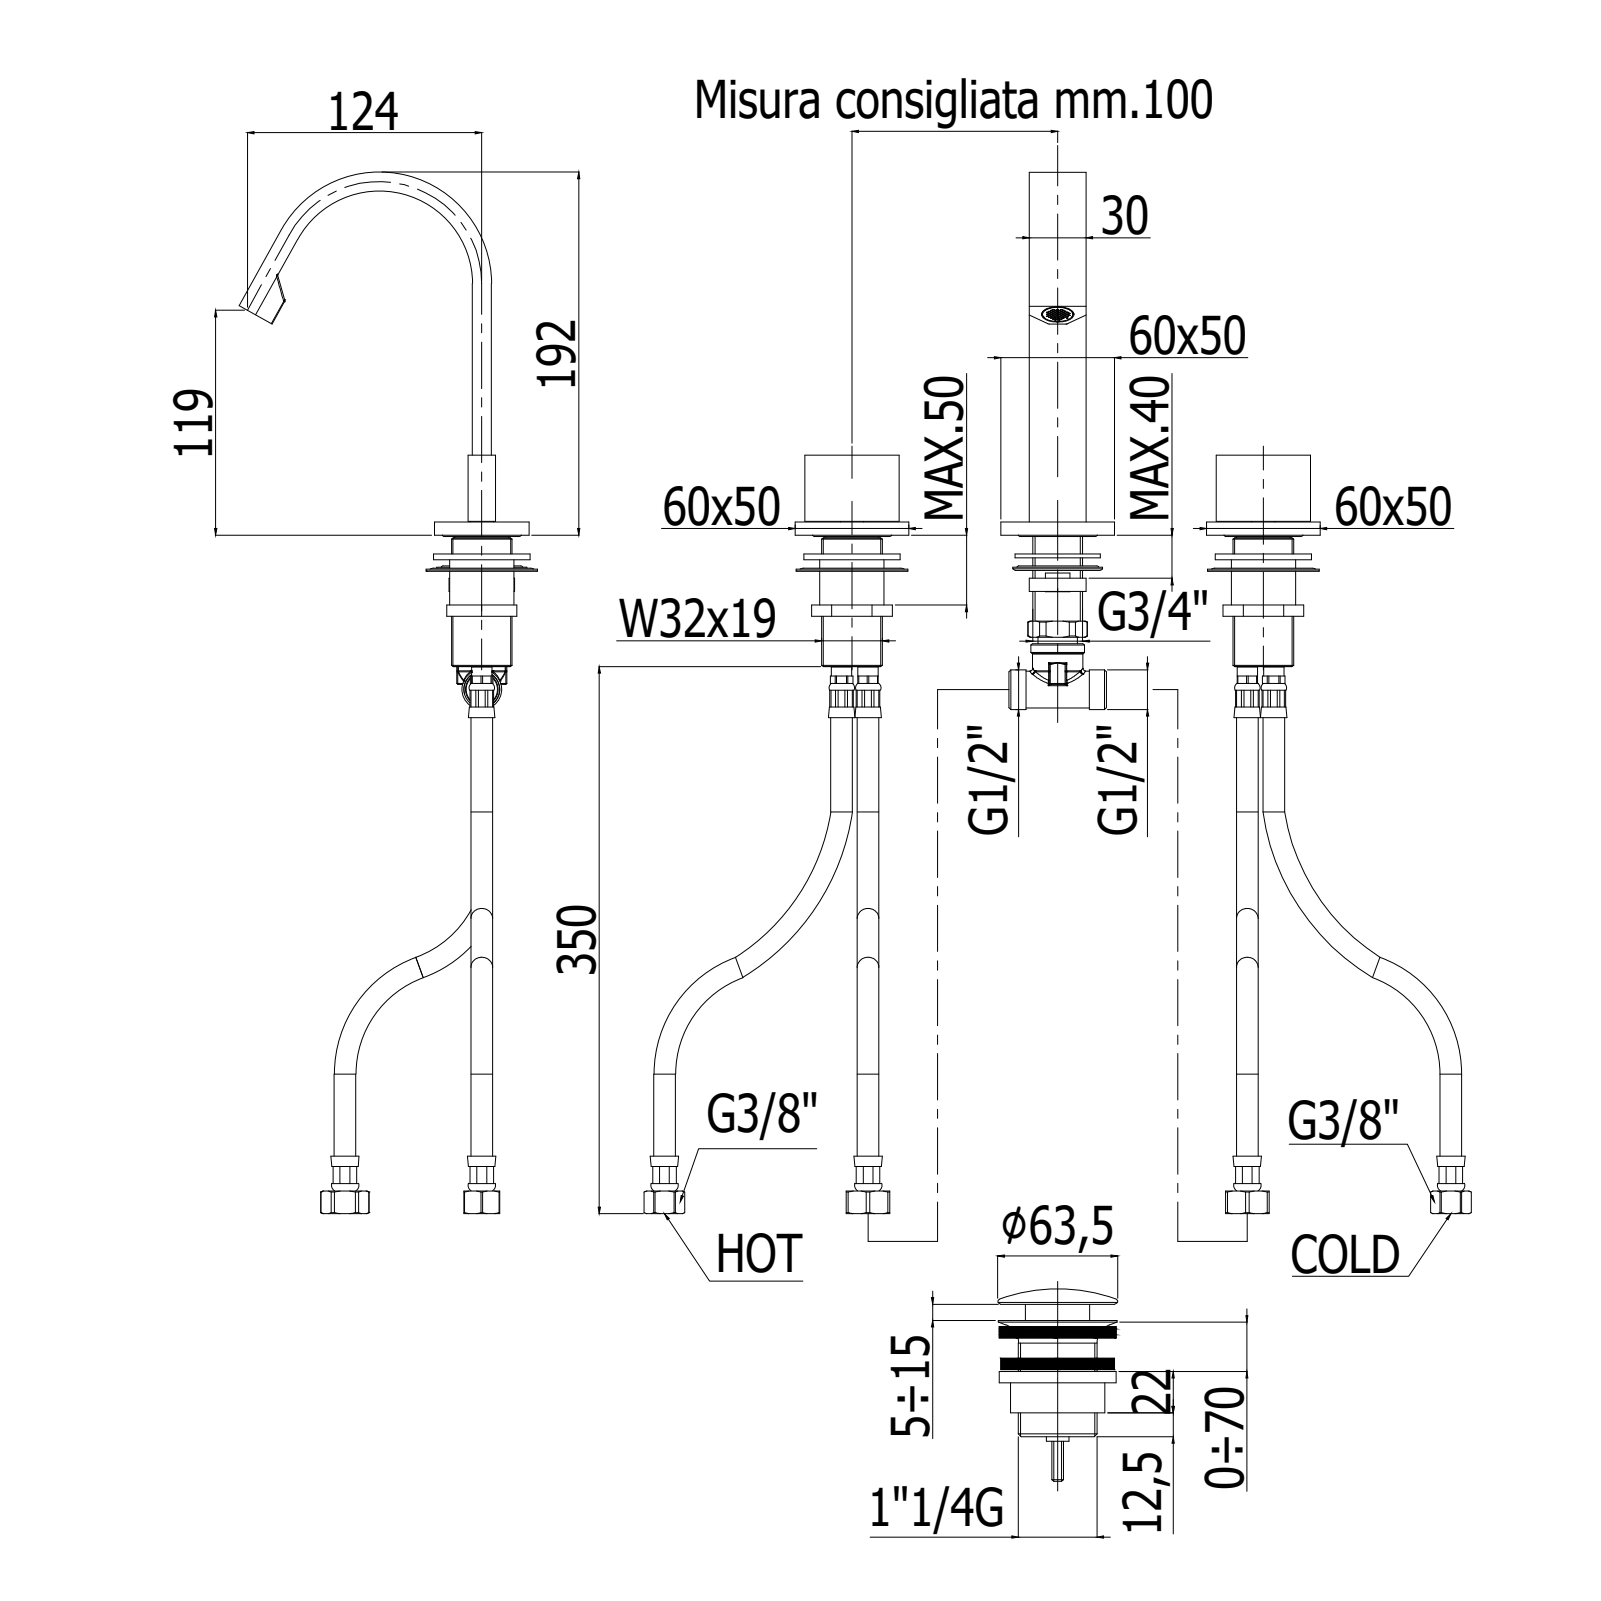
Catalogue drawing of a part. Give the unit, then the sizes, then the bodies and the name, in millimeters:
Units: millimetres
Overall size (bounding box): 360 × 199 × 157.83
Round holes (diameter × count): ⌀4.2 ×4, ⌀3.5 ×3, ⌀42 ×3, ⌀7 ×2, ⌀9 ×2, ⌀9.6 ×2, ⌀10 ×2, ⌀12.5 ×2, ⌀29 ×2, ⌀32 ×2, ⌀5 ×1, ⌀6 ×1
Round bosses / shafts (diameter × count): ⌀38.5 ×3, ⌀0.9 ×3, ⌀12.4 ×2, ⌀6.8 ×2, ⌀16.4 ×1, ⌀16.38 ×1, ⌀15.17 ×1, ⌀15.15 ×1
Partial cylindrical surfaces — rounded edges, fillets, slot ends (radius × count): R0.12 ×51, R0.6 ×4, R1.9 ×3, R7.46 ×1, R52.49 ×1, R53.99 ×1, R60.99 ×1, R62.49 ×1
Main face-to-face distances: 1.5, 7, 8.5, 2.25, 12.25, 28.5, 10.75, 3.75, 30, 10
Hole centre spacings: 300, 10.8, 11.2, 138.8, 150, 161.2, 300.19, 22.4
Volume: 143 611 mm³ · Surface area: 88 047 mm²
Bodies: 4 solids, 2587 faces (1952 planar, 406 cylindrical, 229 other)
Part name (STEP PRODUCT): LEP053CR
STEP written by: CREO PARAMETRIC BY PTC INC, 2020044 (CONFIG_CONTROL_DESIGN)
